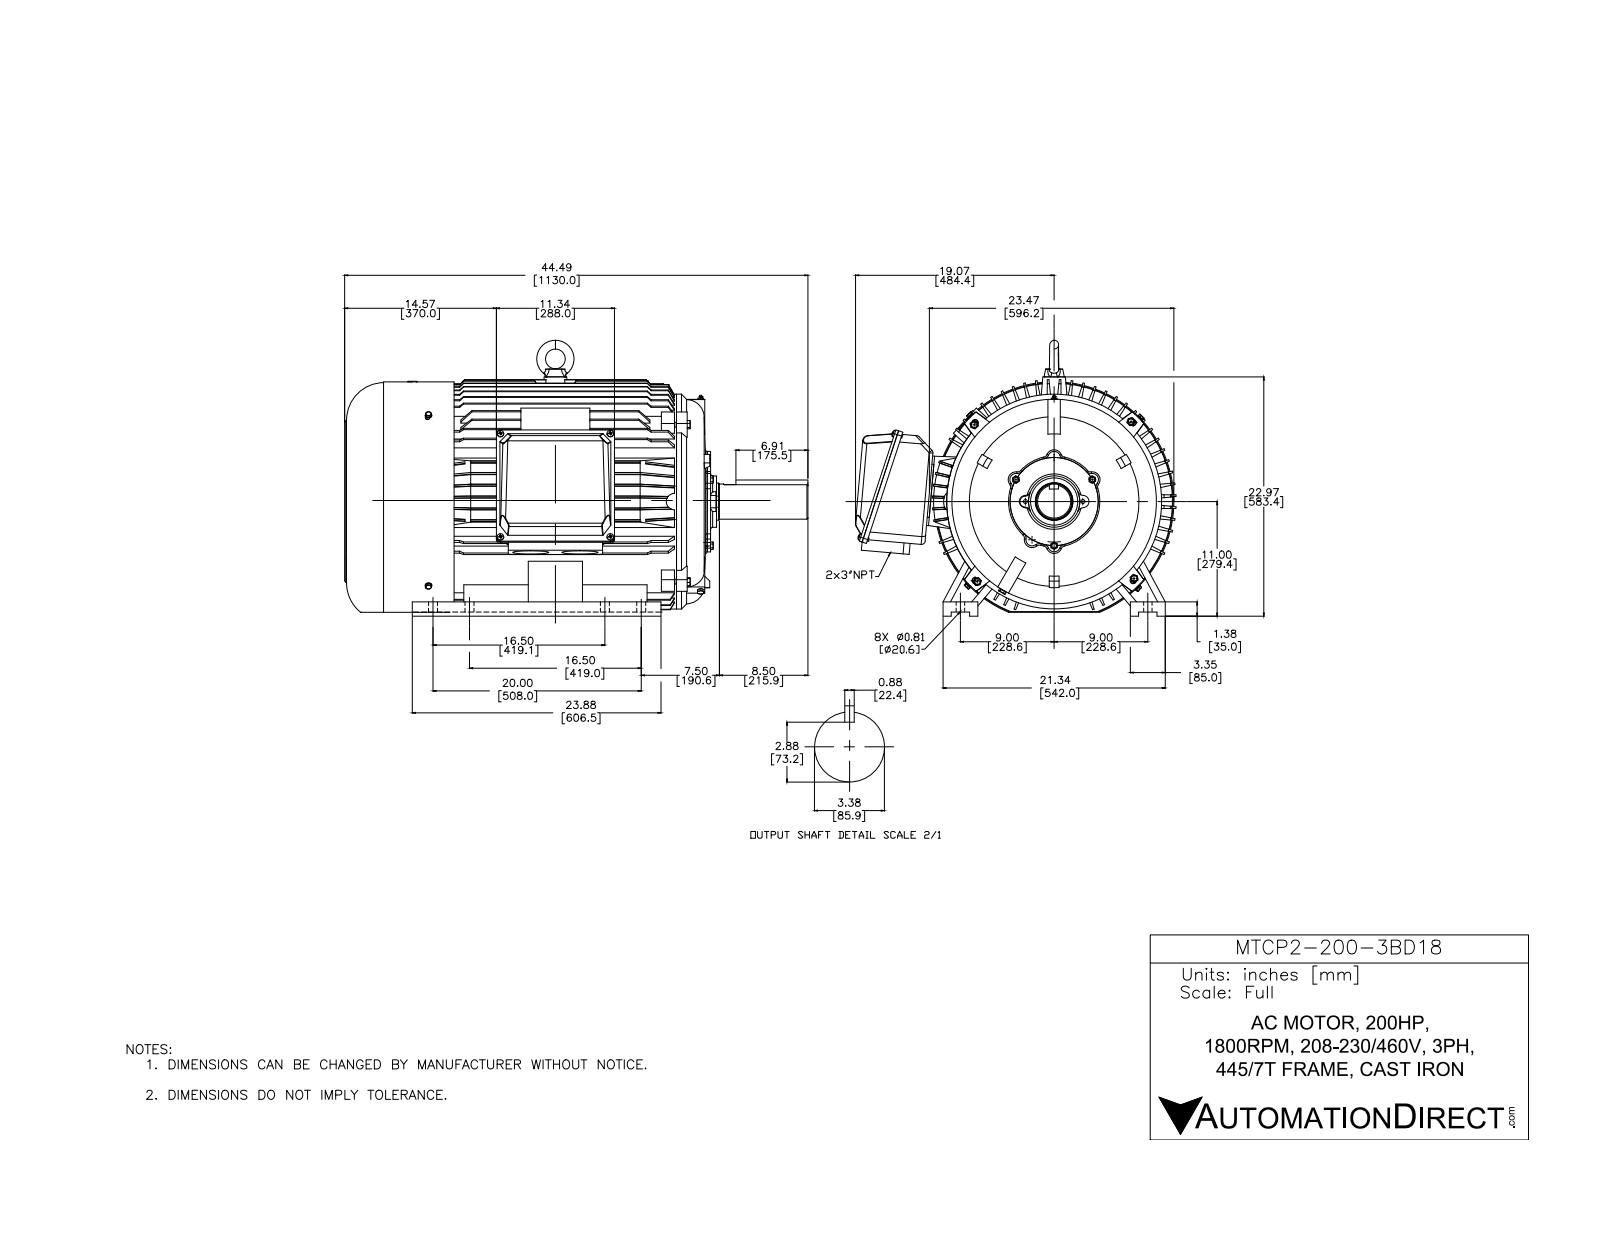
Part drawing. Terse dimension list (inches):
name: PEWWE-445,7T-468P
written by: SolidWorks 2017 (AUTOMOTIVE_DESIGN)
unit: in
bodies: 42 solids, 3965 faces (3151 planar, 458 cylindrical, 356 other)
size: 48.031 × 30.775 × 26.488
volume: 3 162 in³; area: 10 986 in²
holes: 12× ⌀0.315, 8× ⌀0.827, 4× ⌀0.331, 4× ⌀0.539, 4× ⌀0.542, 4× ⌀0.591, 3× ⌀0.472, 2× ⌀0.276, 2× ⌀0.335, 2× ⌀3.465, 1× ⌀0.453, 1× ⌀0.748
bosses: 8× ⌀0.63, 8× ⌀0.315, 4× ⌀0.472, 4× ⌀0.428, 3× ⌀0.394, 1× ⌀22.989, 1× ⌀20.63, 1× ⌀10.039
rounds: 23× R0.591, 16× R0.012, 11× R0.354, 10× R0.079, 8× R0.197, 8× R0.394, 4× R0.787, 2× R0.236
face distances: 35.276, 0.059, 35.335, 0.079, 0.039, 0.236, 38.248, 0.984, 0.394, 1.378
hole spacings: 10.551, 3.5, 5.118, 14.838, 15.172, 16.5, 18, 18.337
